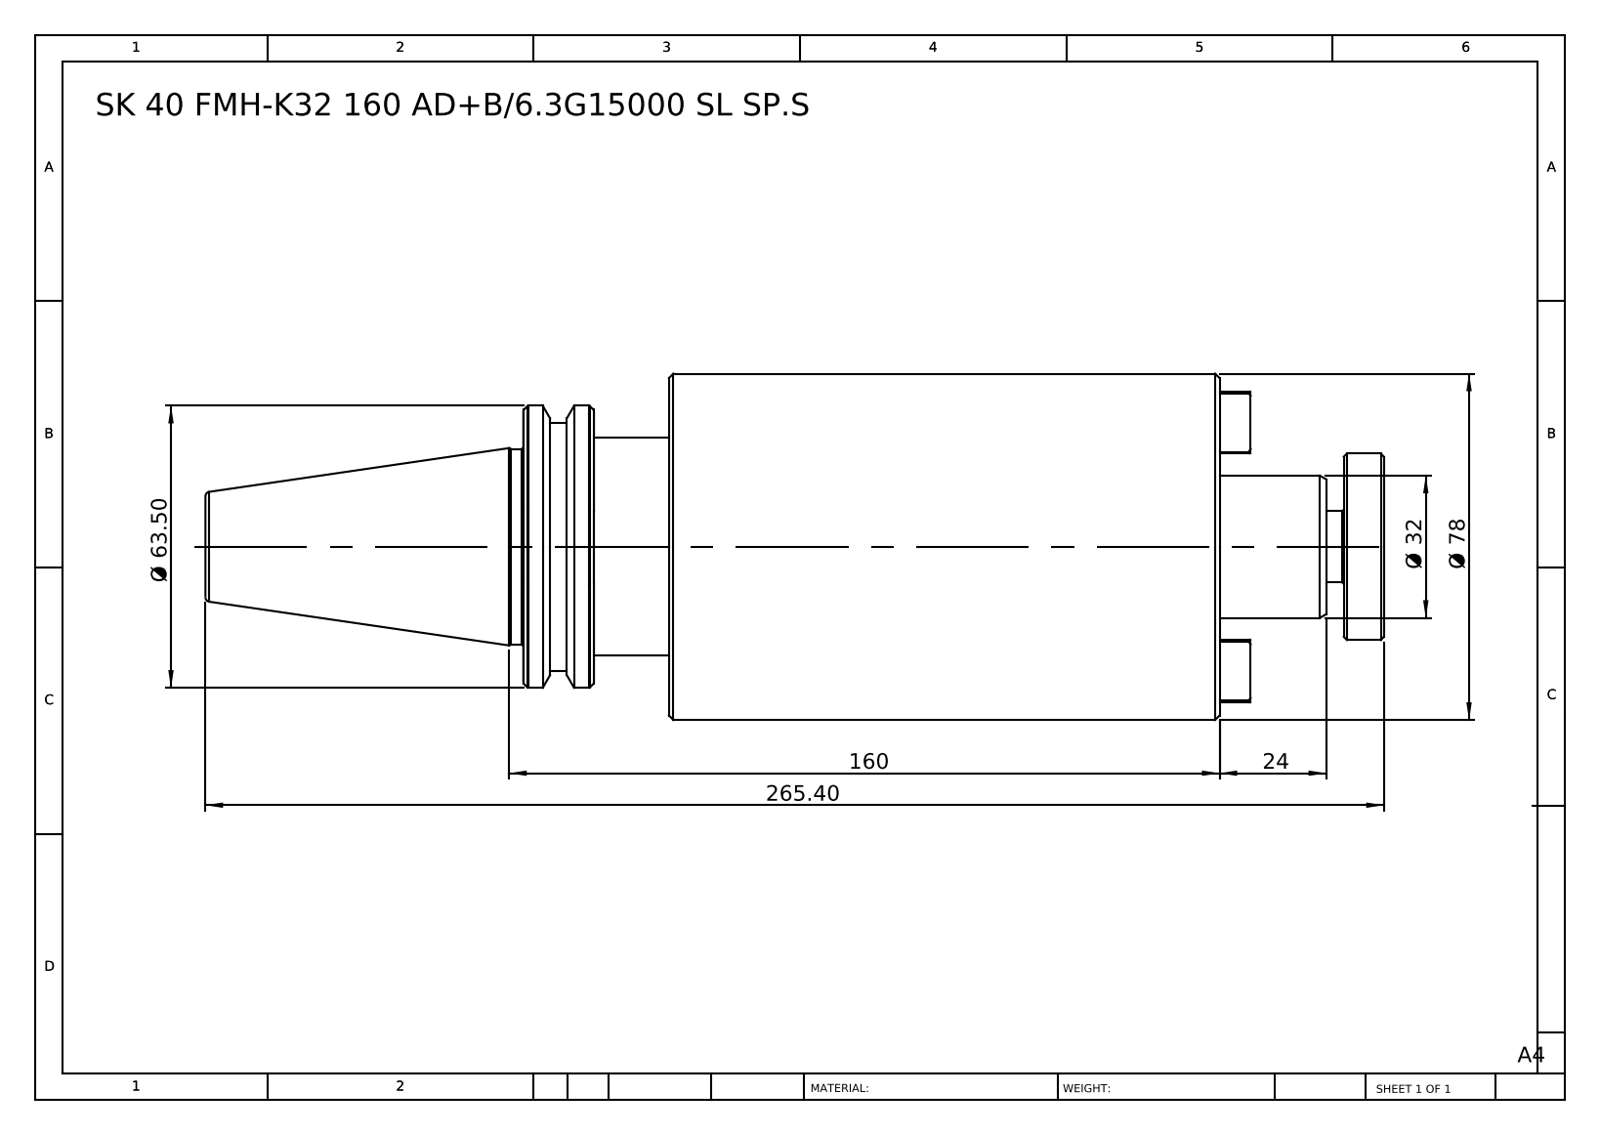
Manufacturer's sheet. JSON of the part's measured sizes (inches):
{"part_name": "SK40 FMH32 160 AD-6.3G15000 SL SP.S", "step_written_by": "SolidWorks 2014 (CONFIG_CONTROL_DESIGN)", "units": "inches", "bodies": {"solids": 1, "faces": 110, "planar": 36, "cylindrical": 18, "other": 56}, "overall_size": [10.449, 3.071, 3.071], "volume_in3": 47.38, "surface_area_in2": 96.36, "round_bosses_or_shafts": [[3.071, 1], [2.5, 1], [2.205, 1], [1.929, 1], [1.732, 1], [1.654, 1], [1.26, 1], [0.63, 1]], "face_to_face_distances": [4.882, 6.173, 1.291, 1.457, 6.339, 7.63, 1.102, 0.354, 5.984, 7.276]}
